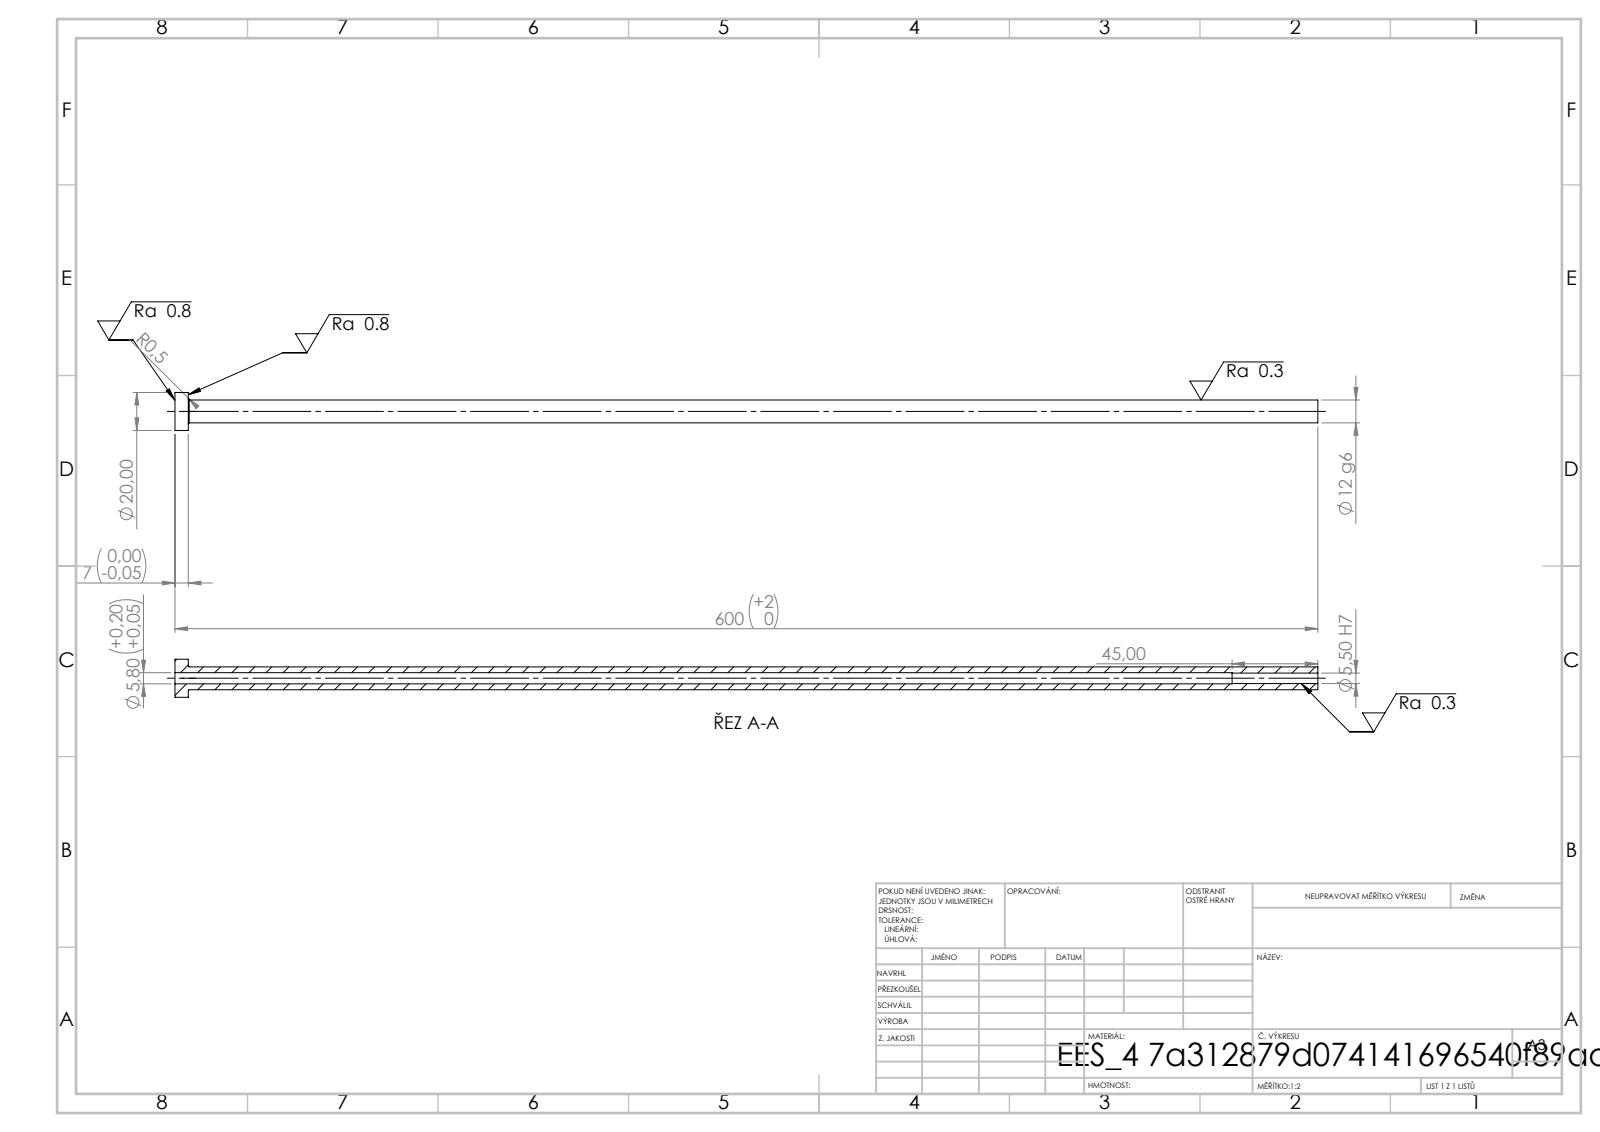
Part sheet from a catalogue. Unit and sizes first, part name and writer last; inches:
Units: inches
Overall size (bounding box): 23.622 × 0.787 × 0.787
Round holes (diameter × count): ⌀0.217 ×1, ⌀0.228 ×1
Round bosses / shafts (diameter × count): ⌀0.787 ×1, ⌀0.472 ×1
Main face-to-face distances: 0.276, 23.622, 23.346, 21.85, 21.575, 1.772
Volume: 3.267 in³ · Surface area: 53.1 in²
Bodies: 1 solid, 14 faces (4 planar, 8 cylindrical, 2 other)
STEP written by: SolidWorks 2019 (CONFIG_CONTROL_DESIGN)
